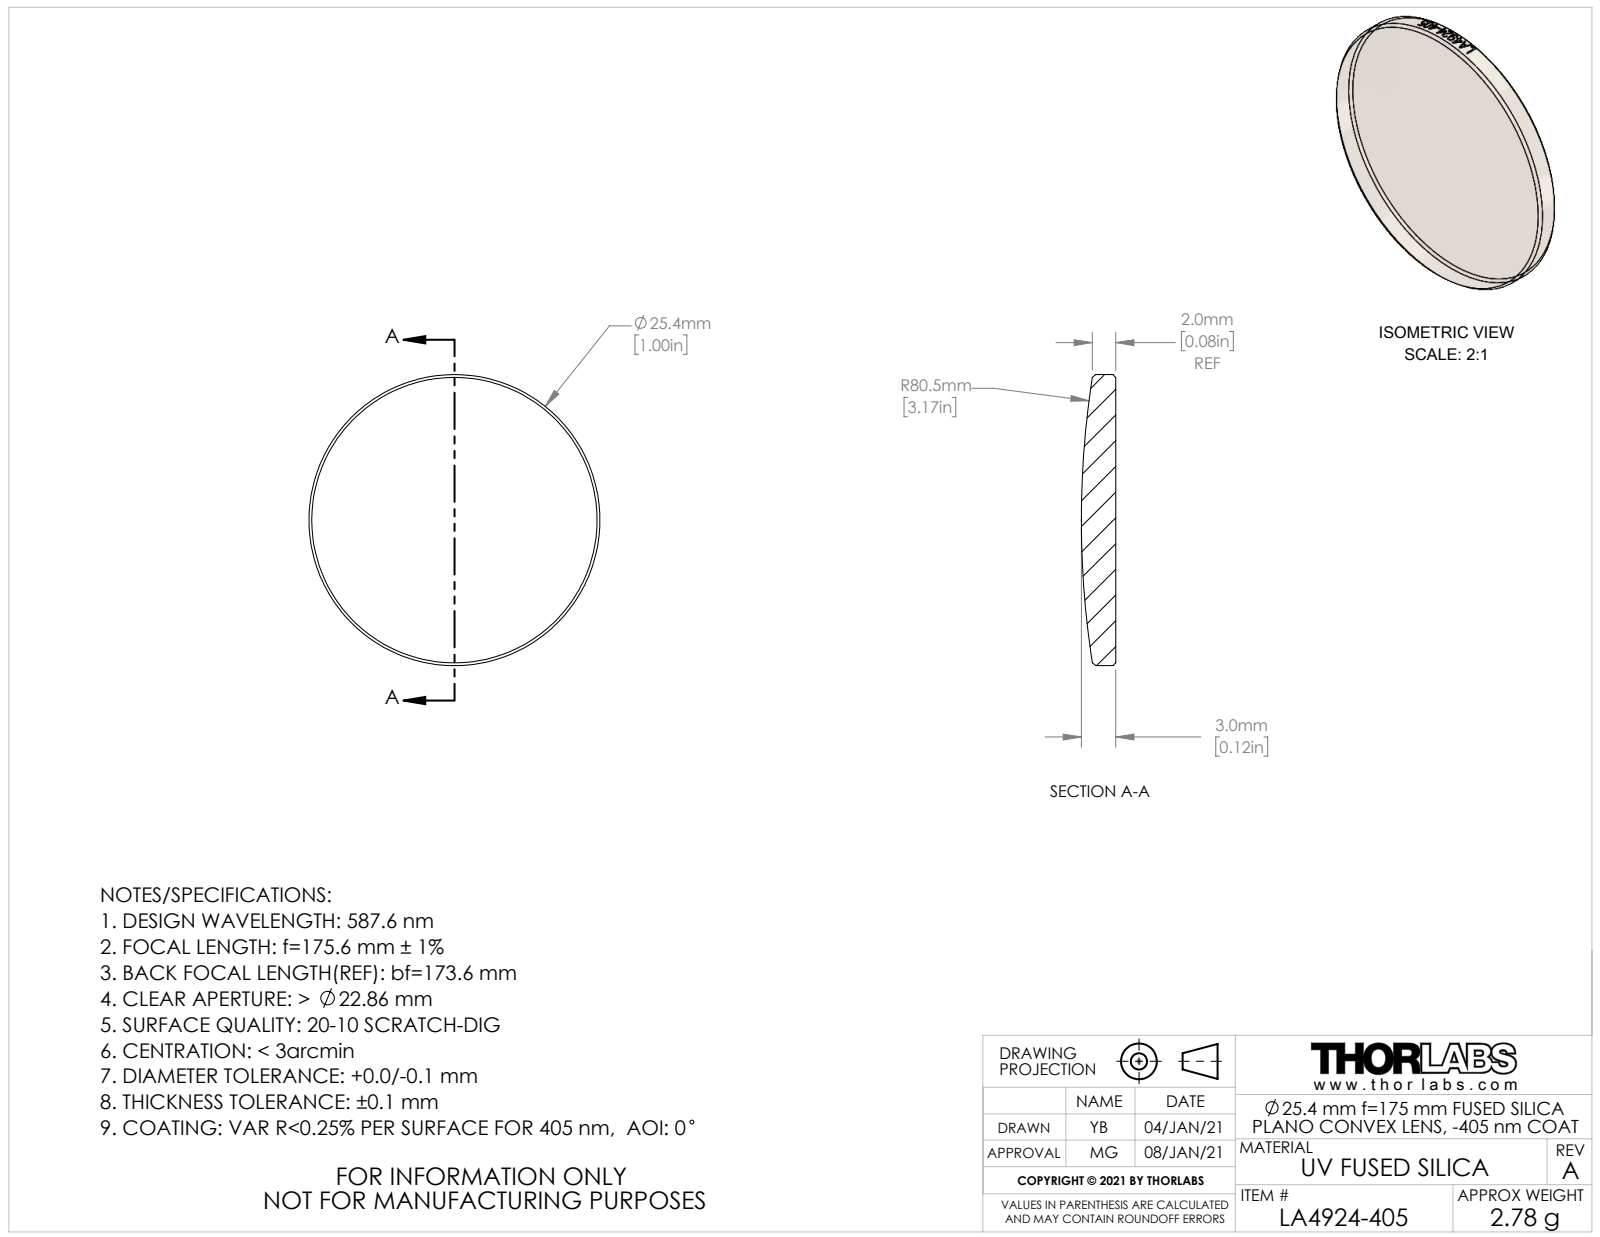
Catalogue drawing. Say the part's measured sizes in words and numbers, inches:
The part is named "CTN016811-E0W; CTN016831". Its 3-D file was written by "SolidWorks 2018 (AUTOMOTIVE_DESIGN)". It is 1 solid with 30 faces: 1 planar, 23 cylindrical and 6 other. Overall it measures 1 by 1 by 0.118 inches. Its volume is 0.077 cubic inches and its surface area 1.79 square inches. Round bosses or shafts: 1 of diameter 1.
